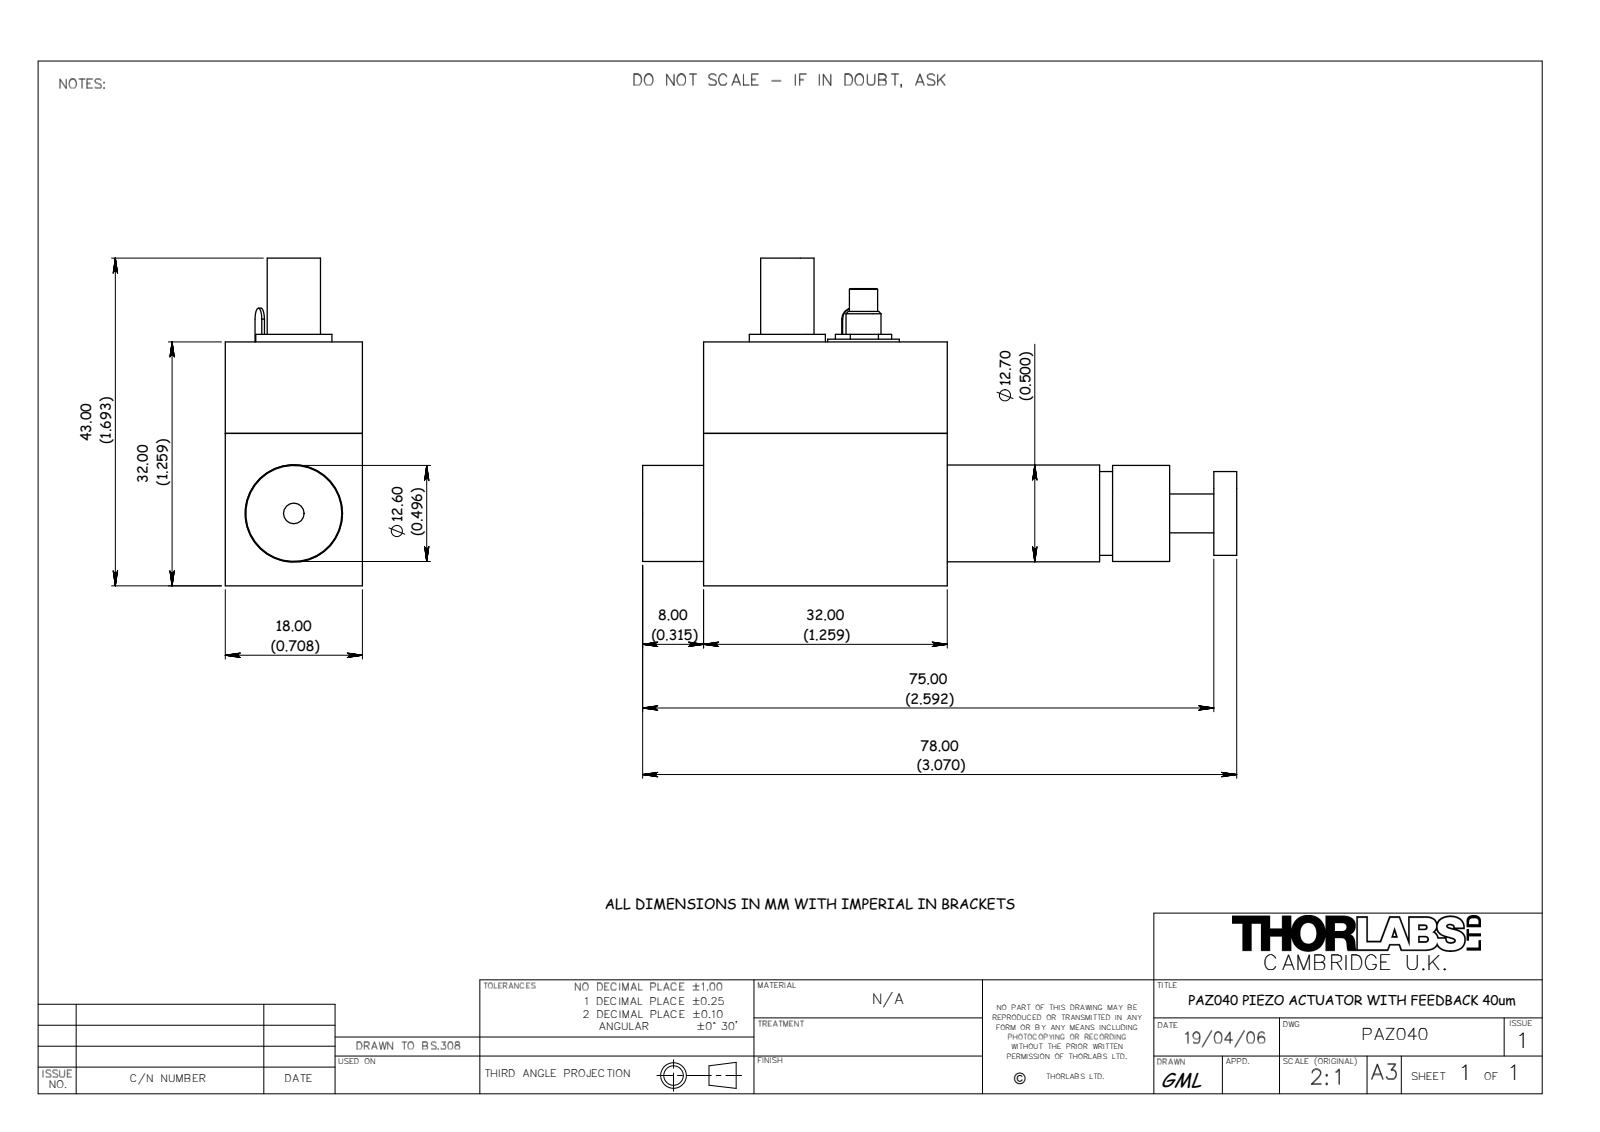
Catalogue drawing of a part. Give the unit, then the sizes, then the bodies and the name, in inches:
Units: inches
Overall size (bounding box): 3.071 × 1.693 × 0.709
Round holes (diameter × count): ⌀0.098 ×2, ⌀0.197 ×2, ⌀0.107 ×1, ⌀0.118 ×1, ⌀0.201 ×1, ⌀0.209 ×1, ⌀0.394 ×1, ⌀0.449 ×1, ⌀0.504 ×1
Round bosses / shafts (diameter × count): ⌀0.5 ×1, ⌀0.496 ×1, ⌀0.433 ×1, ⌀0.37 ×1, ⌀0.354 ×1, ⌀0.276 ×1, ⌀0.201 ×1, ⌀0.181 ×1
Partial cylindrical surfaces — rounded edges, fillets, slot ends (radius × count): R0.059 ×2, R0.057 ×1
Main face-to-face distances: 0.709, 1.26, 0.787, 0.472, 0.315, 1.575, 1.15, 2.409, 2.724, 0.346
Hole centre spacings: 0.315, 0.709, 0.394, 1.024
Bodies: 0 solids, 133 faces (65 planar, 52 cylindrical, 16 other)
Part name (STEP PRODUCT): 15665-E0W
STEP written by: SolidWorks 2007 (AUTOMOTIVE_DESIGN)
